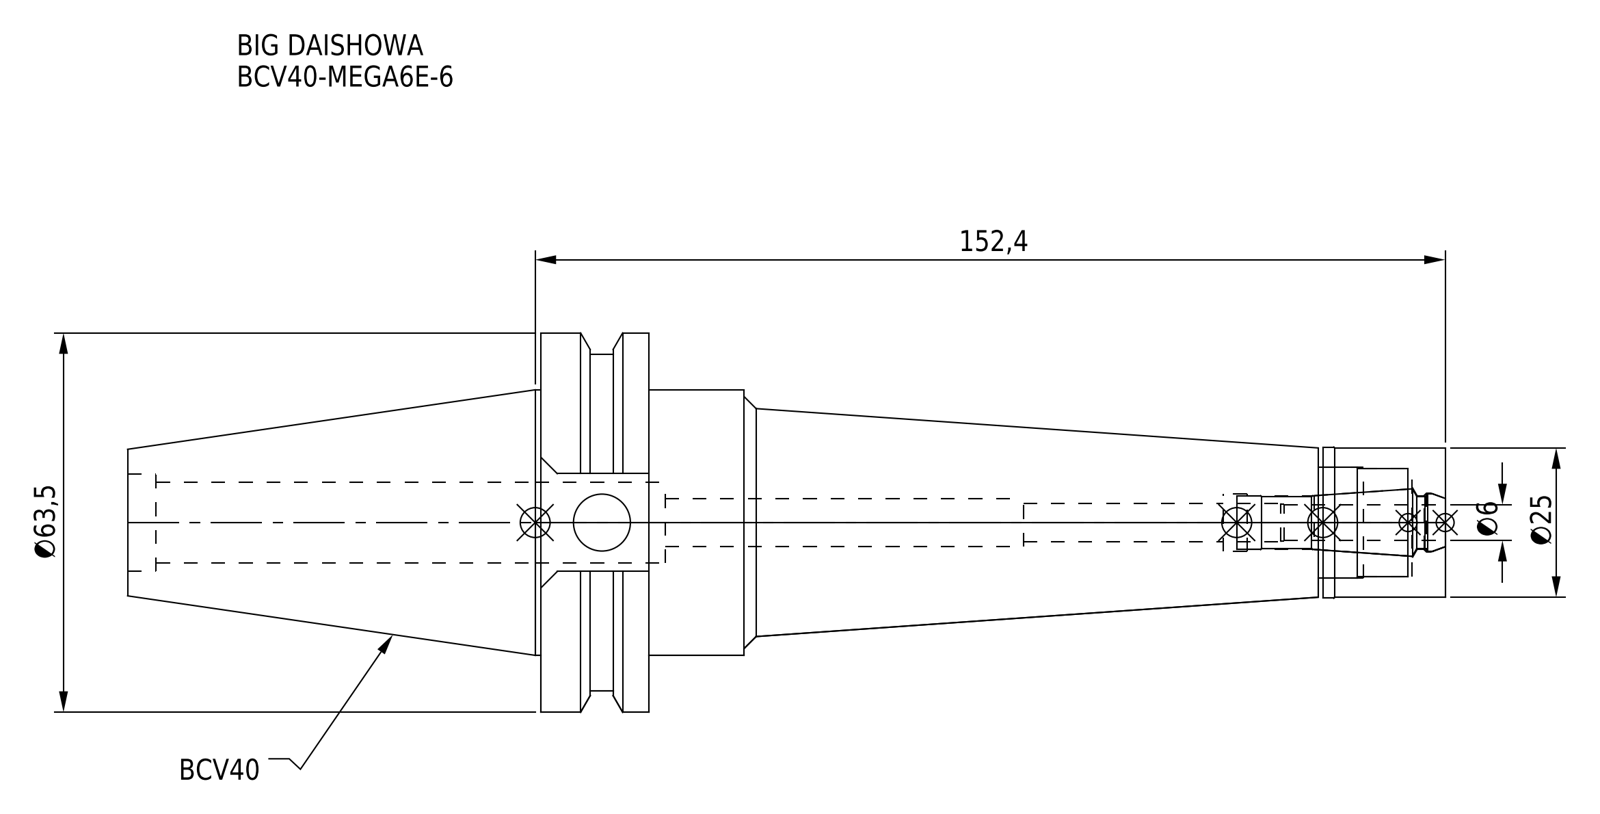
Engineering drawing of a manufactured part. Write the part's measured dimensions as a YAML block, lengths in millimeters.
part_name: "BCV40-MEGA6E-6-060.stp; BCV40-MEGA6E-6_1.stp; BCV40-MEGA6E-6; MEN6_1.stp (+3 more)"
step_written_by: "SolidWorks 2019 (CONFIG_CONTROL_DESIGN)"
units: millimeters
bodies: {solids: 2, faces: 93, planar: 31, cylindrical: 42, other: 20}
overall_size: [220.65, 63.5, 61.35]
volume: 208852
surface_area: 39309
round_holes:
  - {diameter: 6.4, count: 1}
  - {diameter: 8, count: 1}
  - {diameter: 9, count: 1}
  - {diameter: 9.53, count: 1}
  - {diameter: 9.6, count: 1}
  - {diameter: 9.9, count: 1}
  - {diameter: 13.6, count: 1}
  - {diameter: 16.32, count: 1}
  - {diameter: 18, count: 1}
  - {diameter: 18.5, count: 1}
round_bosses_or_shafts:
  - {diameter: 63.5, count: 1}
  - {diameter: 56.36, count: 1}
  - {diameter: 44.45, count: 1}
  - {diameter: 25.3, count: 1}
  - {diameter: 25, count: 1}
face_to_face_distances: [18.05, 133.35, 151.4, 220.65, 87.3, 69.25, 20.5, 112.85, 130.9, 200.15]
